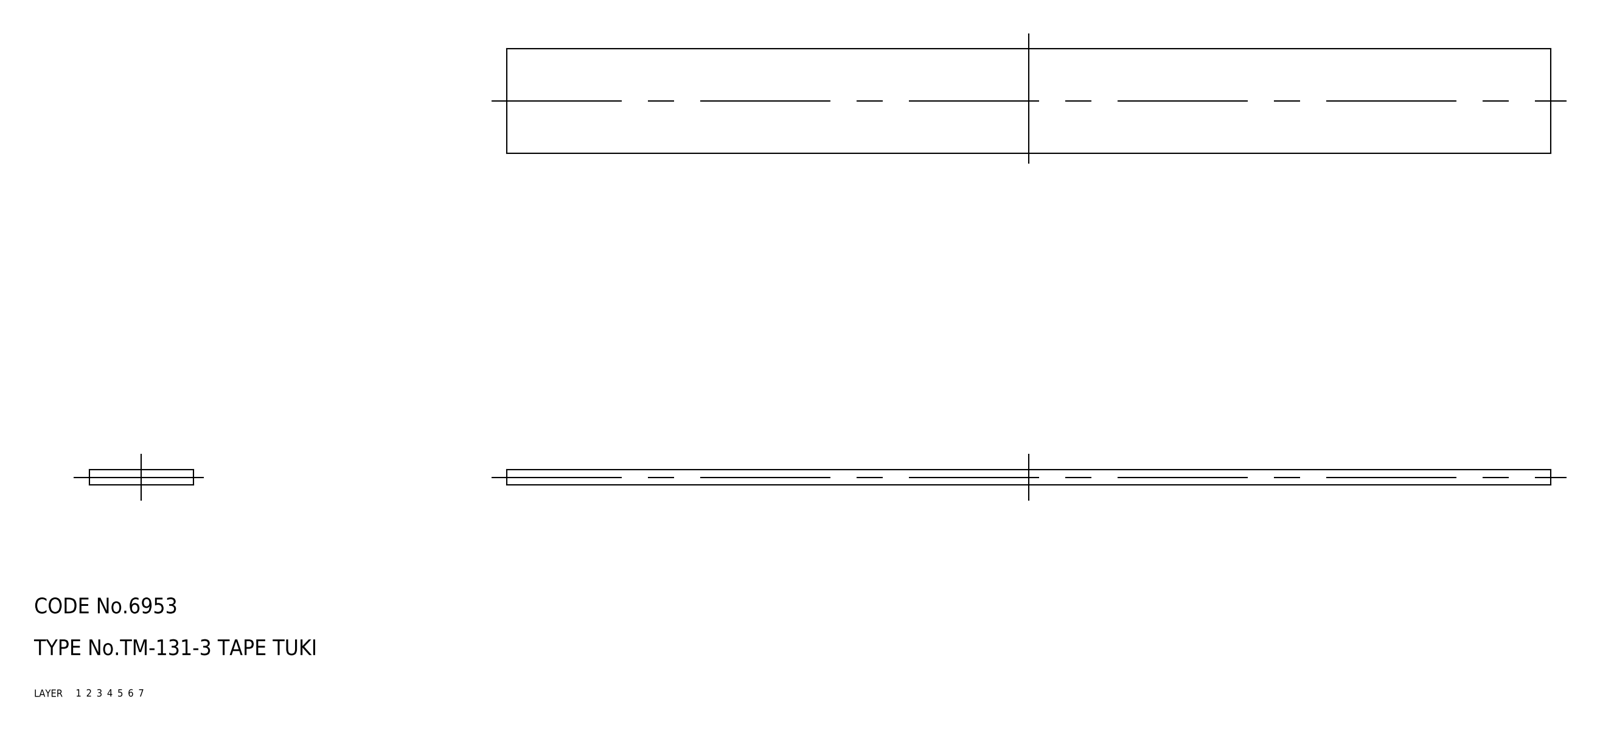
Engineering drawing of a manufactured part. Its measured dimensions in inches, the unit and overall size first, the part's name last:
Units: inches
Overall size (bounding box): 7.874 × 0.787 × 0.118
Volume: 0.732 in³ · Surface area: 14.45 in²
Bodies: 1 solid, 6 faces (0 planar, 0 cylindrical, 6 other)
Part name (STEP PRODUCT): rubber foam
STEP written by: CADfix (AUTOMOTIVE_DESIGN)
